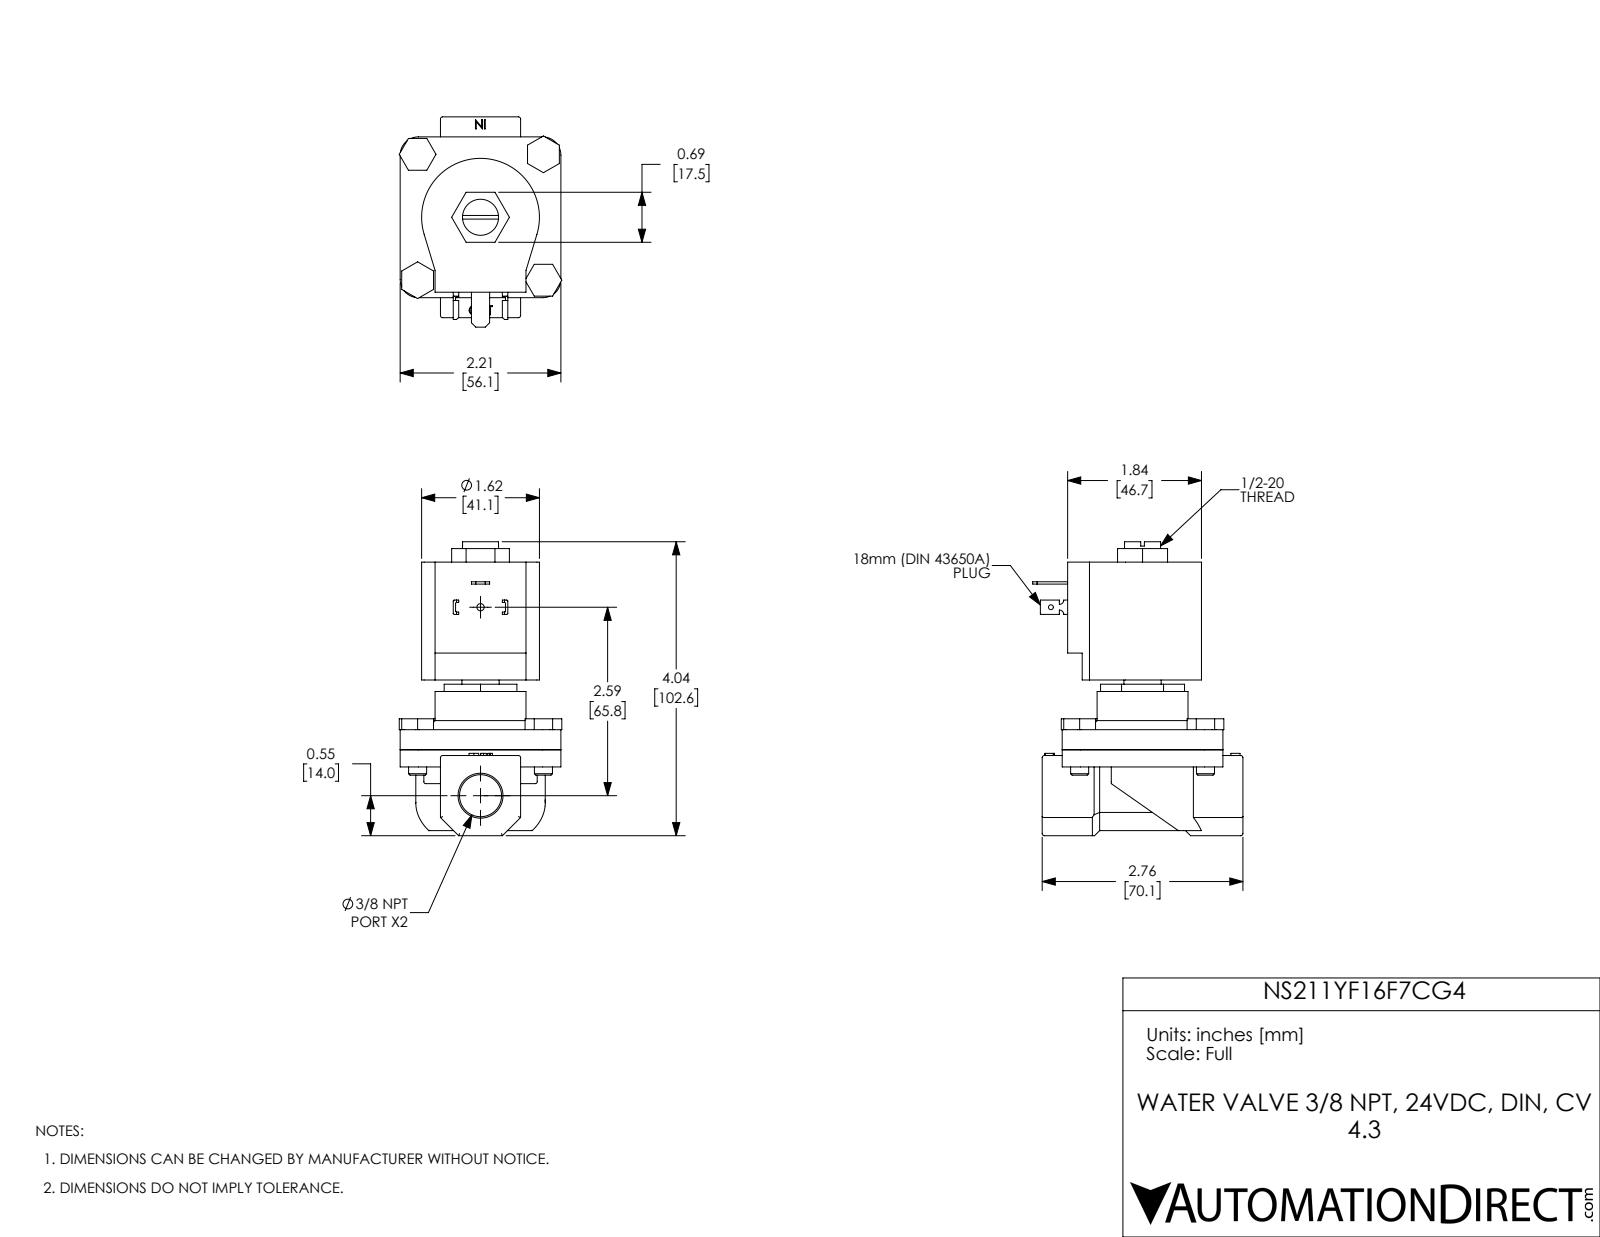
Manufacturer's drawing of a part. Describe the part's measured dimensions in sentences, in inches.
The part is named "NS211YF16F7CG4". Its 3-D file was written by "SolidWorks 2017 (AUTOMOTIVE_DESIGN)". It is 11 solids with 330 faces: 196 planar, 99 cylindrical and 35 other. Overall it measures 4.04 by 2.89 by 2.235 inches. Its volume is 10 cubic inches and its surface area 63.01 square inches. Round holes: 4 of diameter 0.25, 1 of diameter 0.067, 1 of diameter 0.1, 1 of diameter 0.496, 1 of diameter 0.512, 1 of diameter 0.578, 1 of diameter 1.155. Round bosses or shafts: 4 of diameter 0.248, 1 of diameter 1.25. Partial cylindrical surfaces (rounded edges, fillets, slot ends): 15 of radius 0.03, 8 of radius 0.015, 4 of radius 0.25, 2 of radius 0.06, 1 of radius 0.81, 1 of radius 0.89. The main face-to-face distances are 0.276, 2.579, 2.303, 0.554, 1.656, 0.236, 0.512, 2.815, 2.21, 1.102. The hole center spacings are 1.223, 1.73, 2.446, 2.59.
